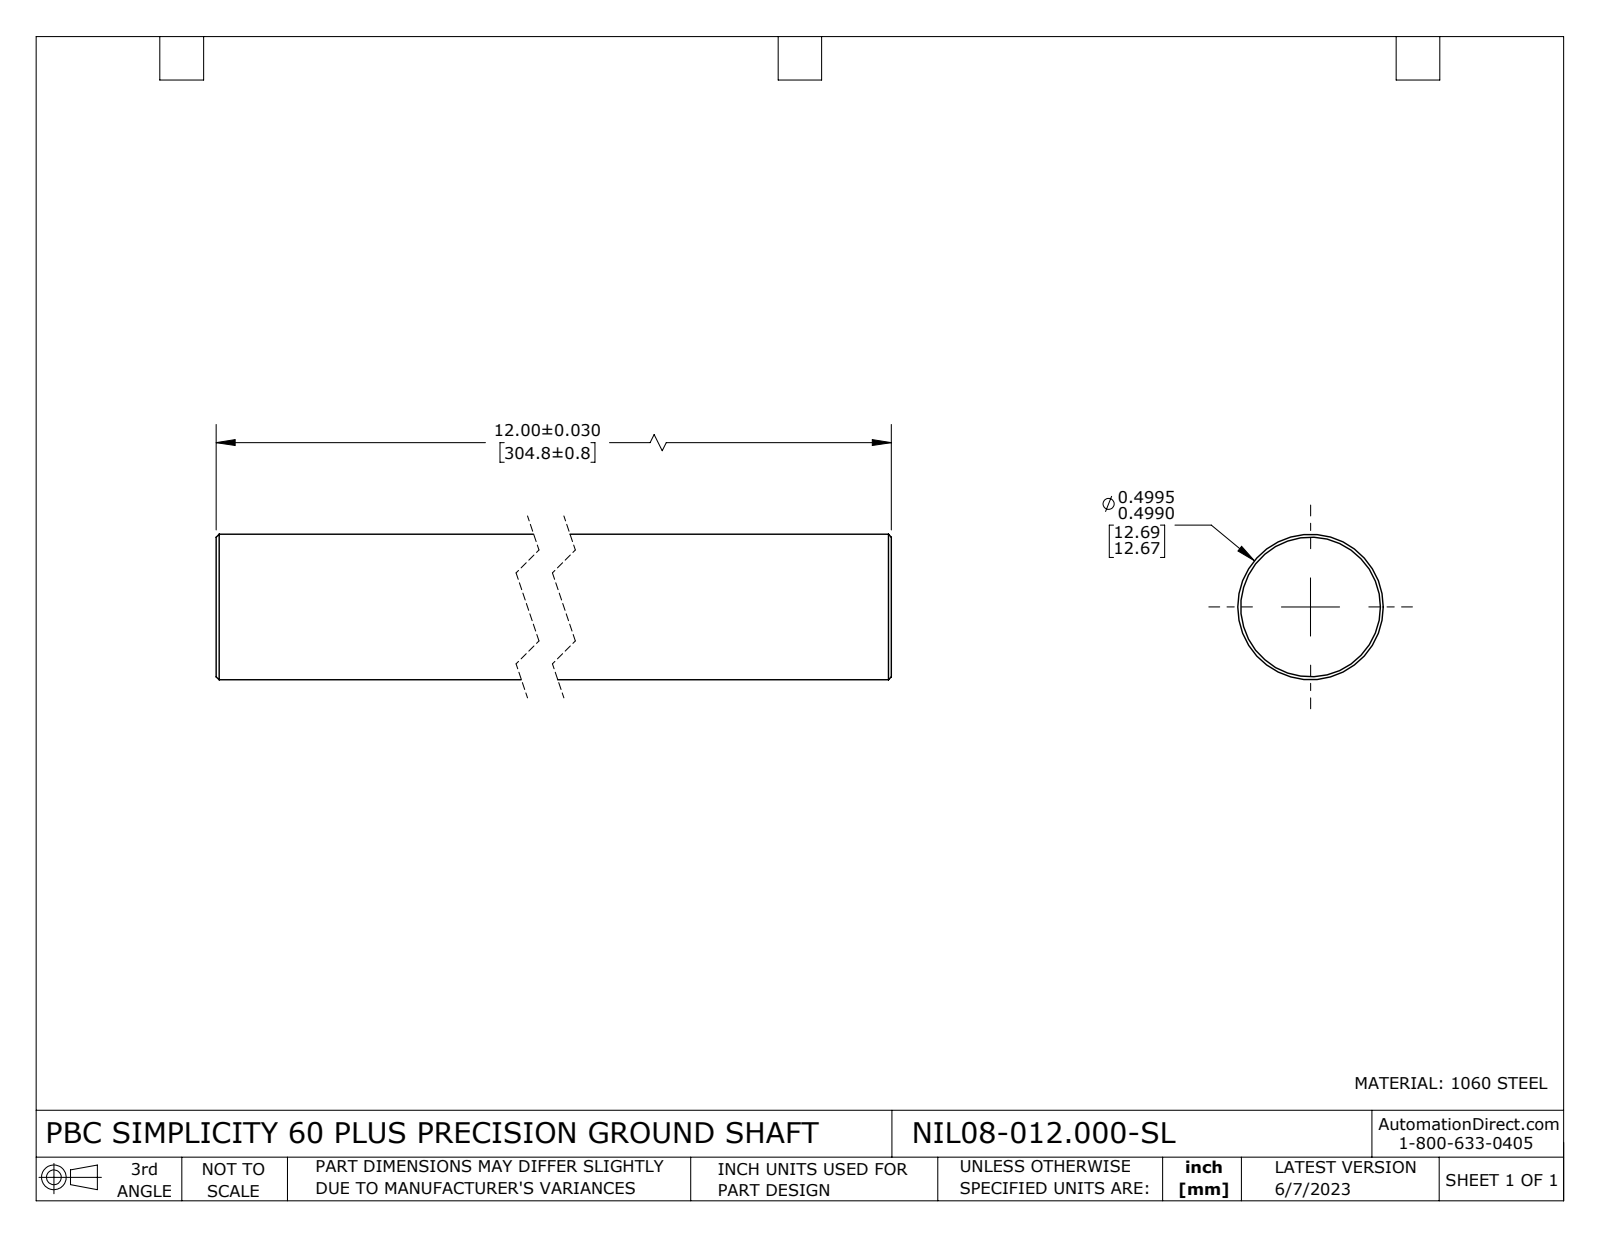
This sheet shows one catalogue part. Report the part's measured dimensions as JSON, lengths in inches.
{"part_name": "NIL08-012.000-SL", "step_written_by": "SolidWorks 2021 (CONFIG_CONTROL_DESIGN)", "units": "inches", "bodies": {"solids": 1, "faces": 8, "planar": 2, "cylindrical": 2, "other": 4}, "overall_size": [12, 0.5, 0.5], "volume_in3": 2.356, "surface_area_in2": 19.22, "round_bosses_or_shafts": [[0.5, 1]], "face_to_face_distances": [12]}
